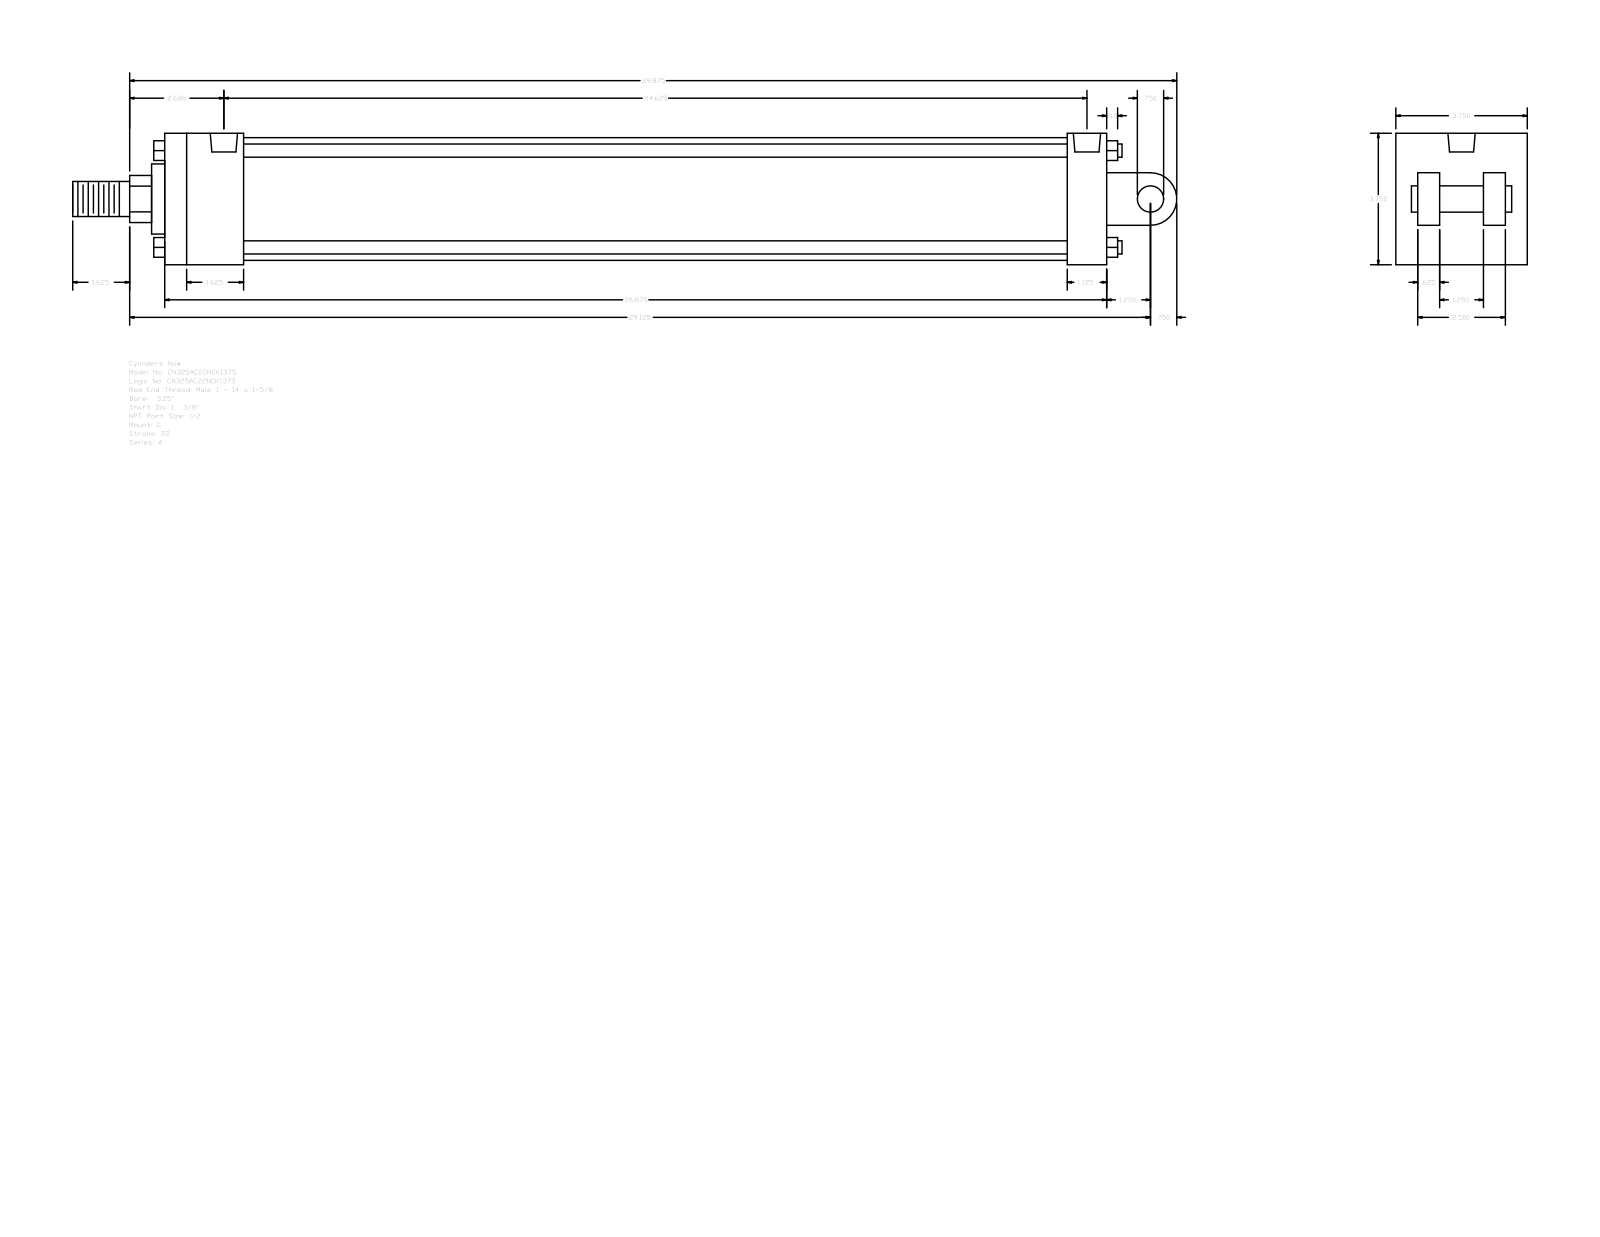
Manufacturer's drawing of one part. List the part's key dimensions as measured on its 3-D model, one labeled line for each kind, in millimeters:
Part name (STEP PRODUCT): A_C__0325_1.375
STEP written by: GSSL Pune (CONFIG_CONTROL_DESIGN)
Units: millimetres
Bodies: 0 solids, 135 faces (102 planar, 33 cylindrical, 0 other)
Overall size (bounding box): 800.1 × 95.25 × 95.25
Round holes (diameter × count): ⌀8.73 ×4, ⌀19.77 ×2
Round bosses / shafts (diameter × count): ⌀9.53 ×4, ⌀88.9 ×1, ⌀50.8 ×1, ⌀34.92 ×1, ⌀25.4 ×1, ⌀19.05 ×1
Partial cylindrical surfaces — rounded edges, fillets, slot ends (radius × count): R17.06 ×1, R19.05 ×1
Main face-to-face distances: 95.24, 682.62, 15.87, 28.57, 63.5, 66.67, 57.15, 31.74, 79.37, 47.63
Hole centre spacings: 3.18, 619.12, 622.3, 625.48
